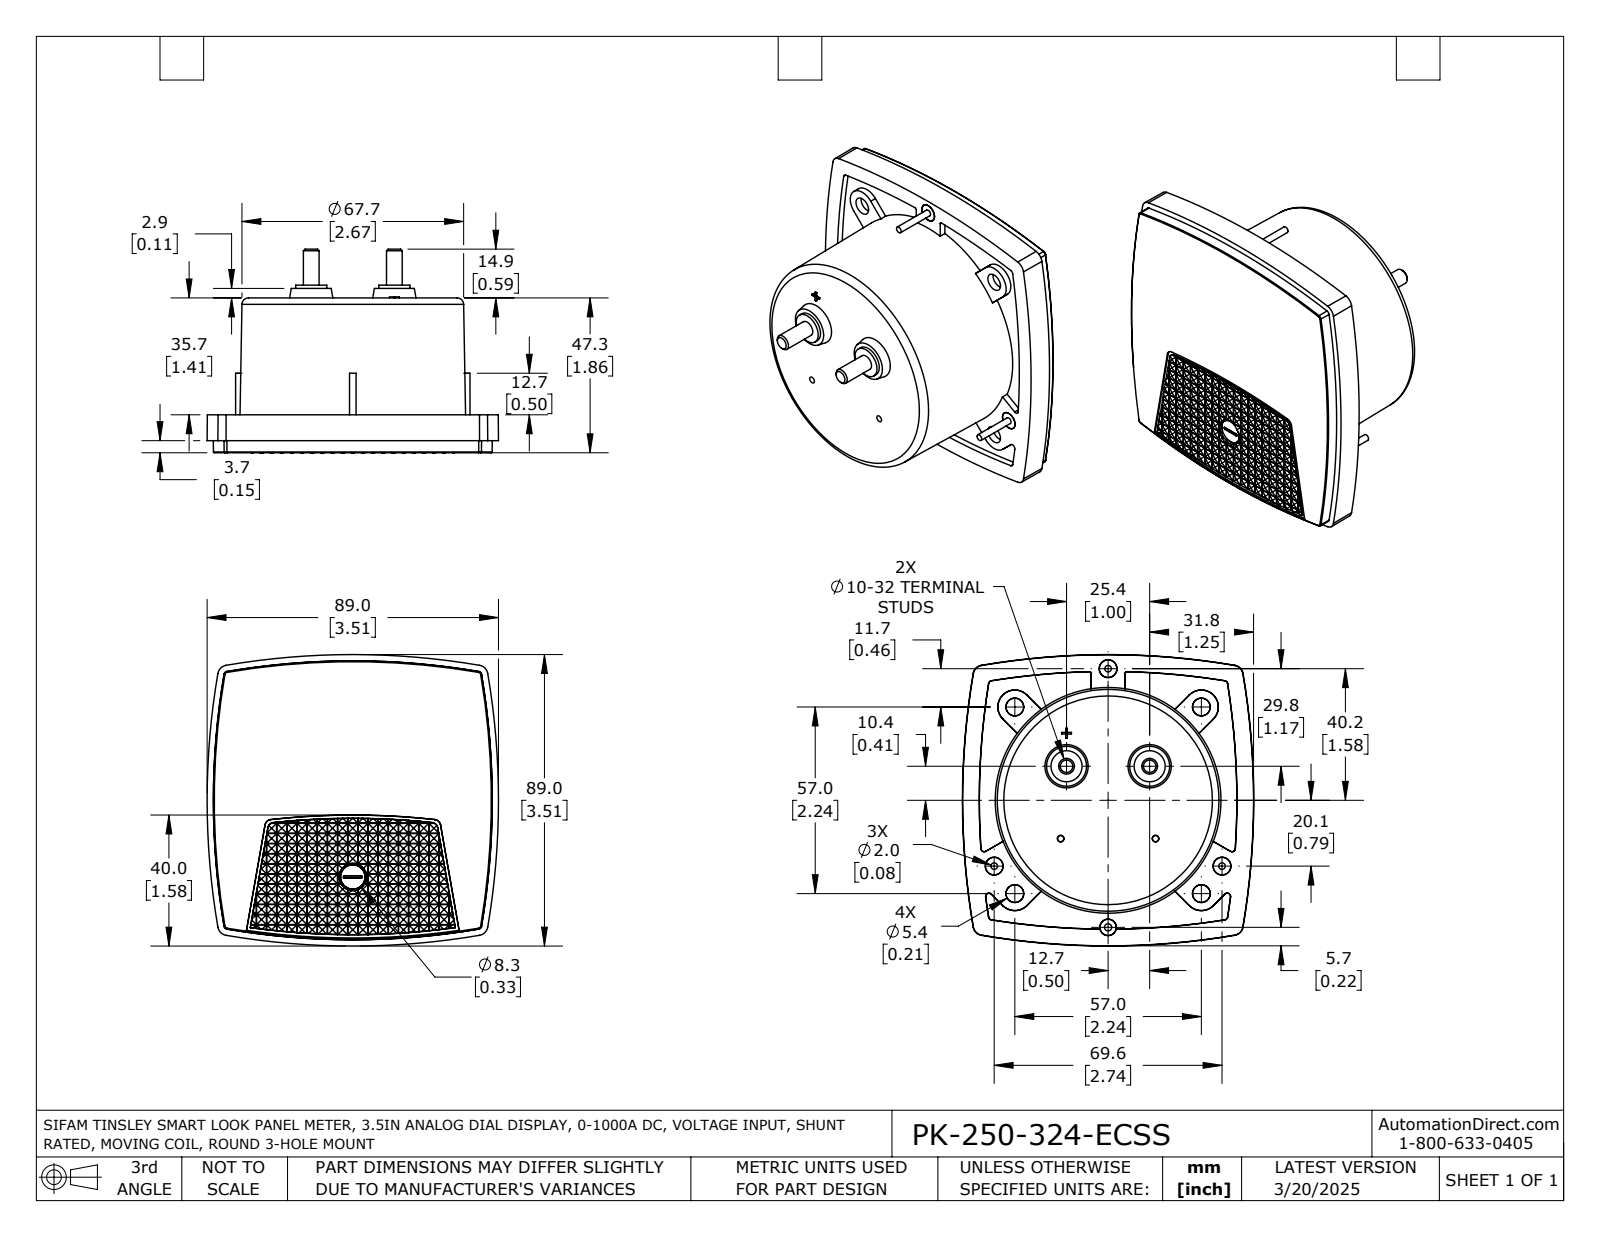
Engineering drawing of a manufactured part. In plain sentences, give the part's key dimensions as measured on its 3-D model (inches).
The part is named "PK-250-324-ECSS". Its 3-D file was written by "SolidWorks 2021 (AUTOMOTIVE_DESIGN)". It is 1 solid with 1078 faces: 950 planar, 23 cylindrical and 105 other. Overall it measures 3.505 by 3.505 by 2.453 inches. Its volume is 12.99 cubic inches and its surface area 44.29 square inches. Round holes: 1 of diameter 0.087. Round bosses or shafts: 3 of diameter 0.213, 3 of diameter 0.079, 2 of diameter 0.374, 2 of diameter 0.189. Partial cylindrical surfaces (rounded edges, fillets, slot ends): 1 of radius 8.961. The main face-to-face distances are 1.862, 1.406, 0.457, 0.079, 1.484, 0.378, 0.024, 0.096, 0.072, 0.12.
